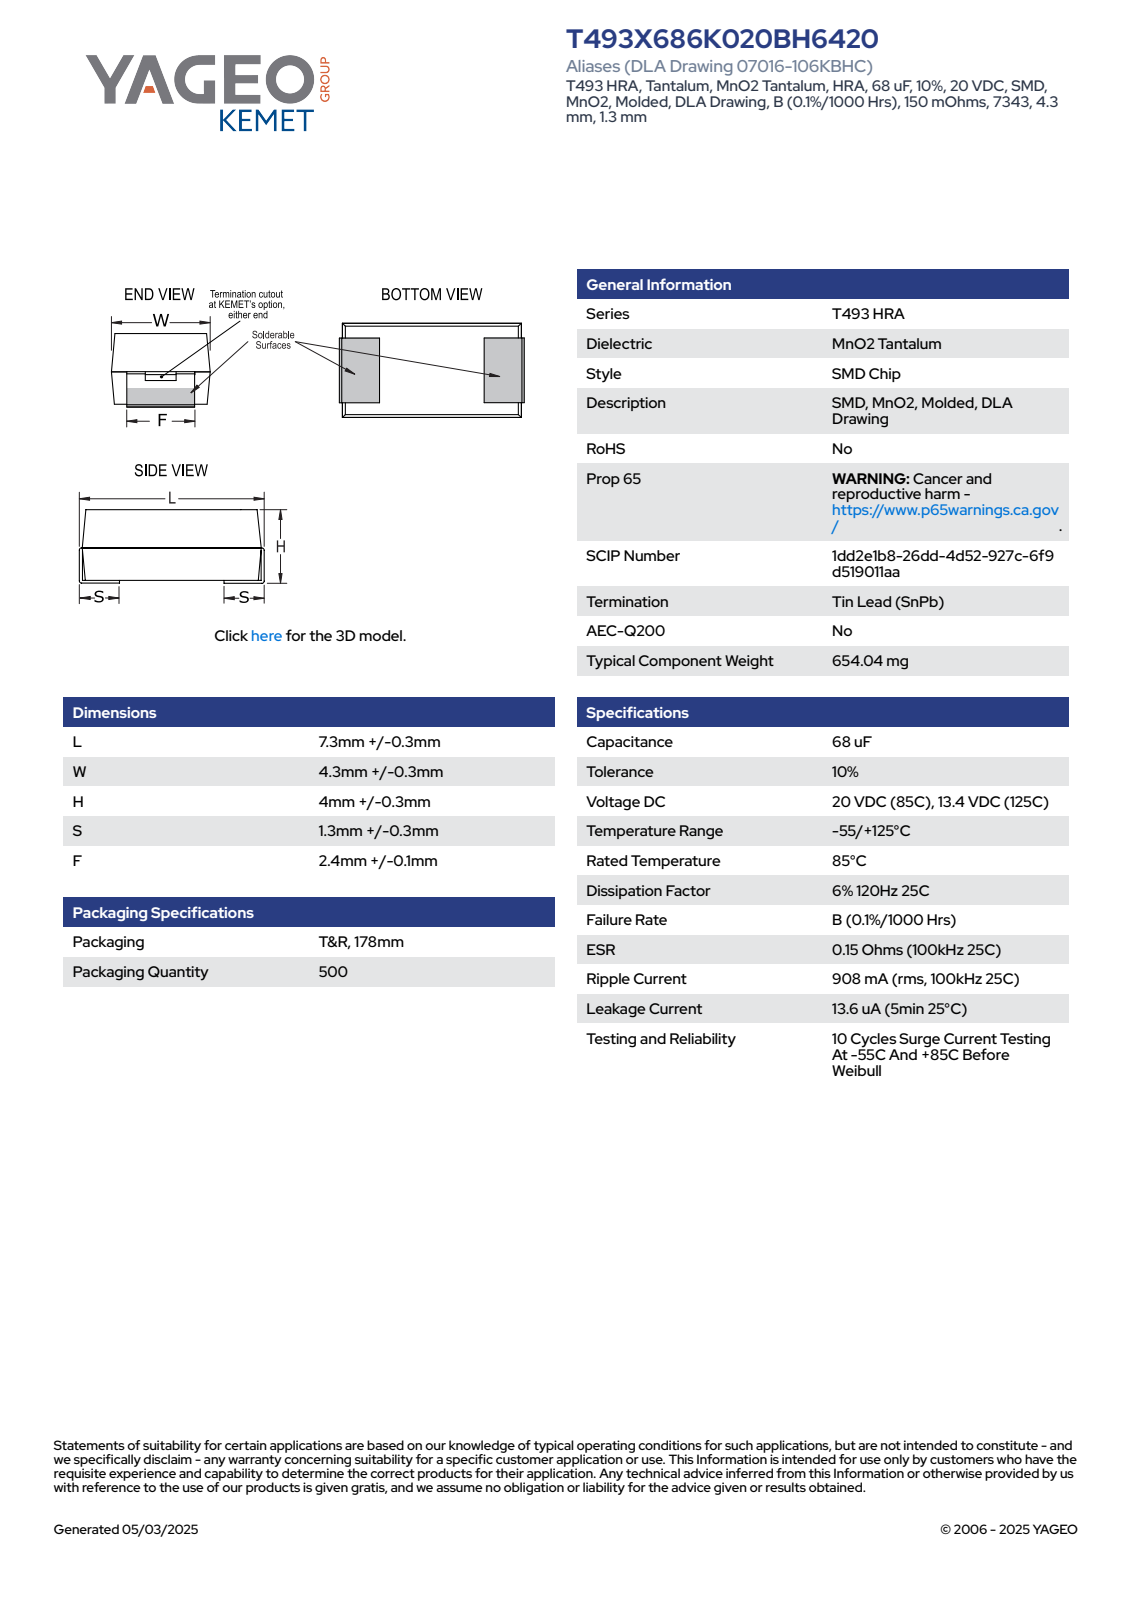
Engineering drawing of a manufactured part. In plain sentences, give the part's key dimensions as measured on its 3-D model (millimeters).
The part is named "CTSM_Case_Top_27; CTSM_Case_Cathode_27; CTSM_7343_L7.60W4.6H4.30S1.3F2.4; CTSM_Case_Bottom_27 (+1 more)". Its 3-D file was written by "SolidWorks 2014 (AUTOMOTIVE_DESIGN)". It is 7 solids with 94 faces: 90 planar, 4 cylindrical and 0 other. Overall it measures 7.6 by 4.6 by 4.3 millimeters. Its volume is 135 cubic millimeters and its surface area 260 square millimeters. The main face-to-face distances are 2.17, 4.58, 2, 4.17, 7.31, 7.47, 2.1, 4.27, 2.13, 4.3.
